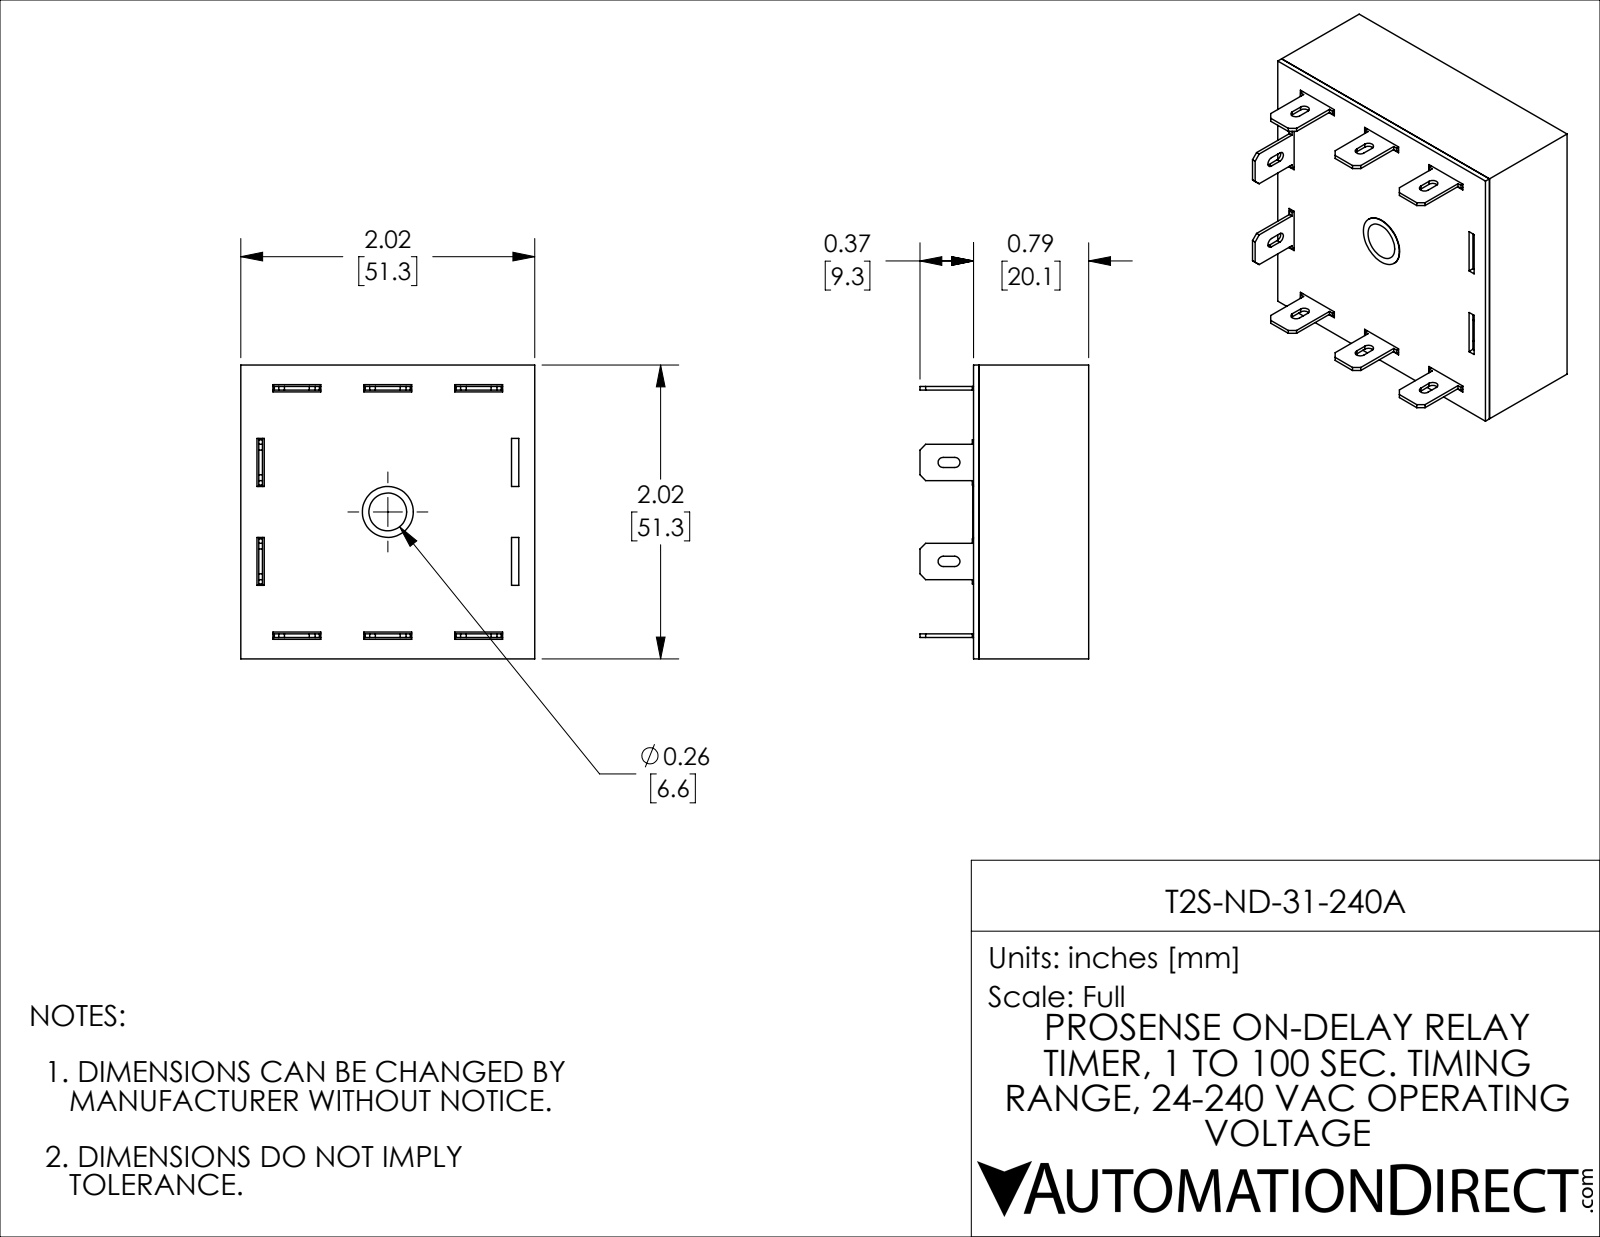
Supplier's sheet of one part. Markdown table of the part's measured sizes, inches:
| quantity | value |
| --- | --- |
| part name | T2S-ND-31-240A |
| STEP written by | SolidWorks 2021 (CONFIG_CONTROL_DESIGN) |
| units | inches |
| bodies | 10 solids, 256 faces (234 planar, 20 cylindrical, 2 other) |
| overall size | 2.02 × 2.02 × 1.16 |
| volume | 0.674 in³ |
| surface area | 35.37 in² |
| round holes (diameter × count) | 0.35 × 1 |
| partial cylindrical surfaces (radius × count) | 0.035 × 10 |
| main face-to-face distances | 0.045, 1.975, 0.754, 0.792, 0.038, 0.709, 0.747, 2.02, 1.93, 0.147 |
